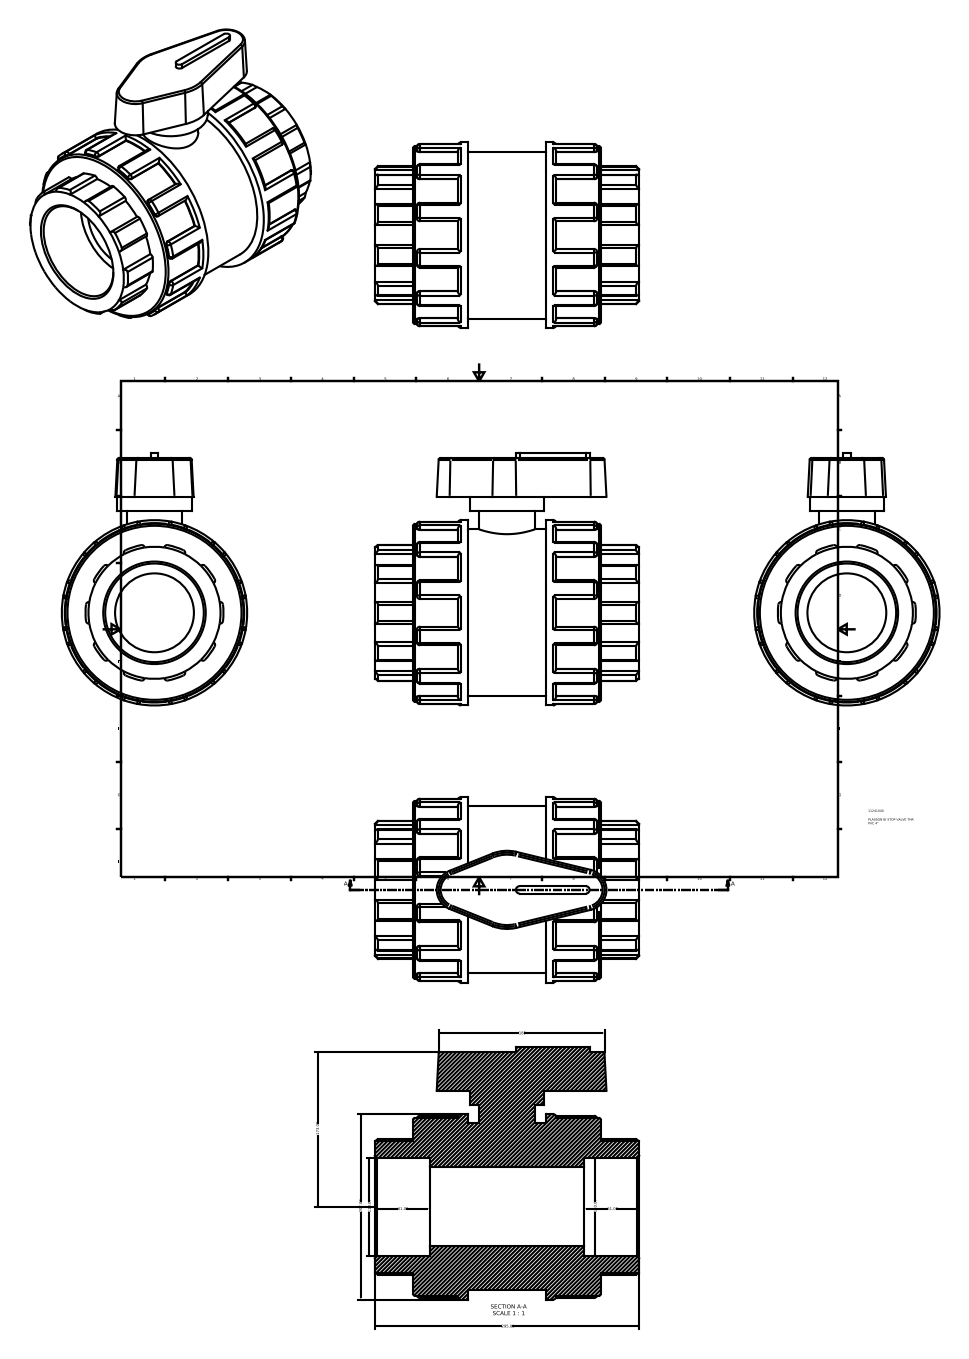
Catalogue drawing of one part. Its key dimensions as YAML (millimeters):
part_name: "11241040"
step_written_by: "Autodesk Inventor 2015 (AUTOMOTIVE_DESIGN)"
units: millimeters
bodies: {solids: 1, faces: 434, planar: 114, cylindrical: 192, other: 128}
overall_size: [295, 281.69, 207]
volume: 6262000
surface_area: 375836
round_holes:
  - {diameter: 88.06, count: 1}
  - {diameter: 110.07, count: 1}
round_bosses_or_shafts:
  - {diameter: 207, count: 1}
  - {diameter: 198.72, count: 1}
  - {diameter: 186.3, count: 1}
  - {diameter: 82.8, count: 1}
  - {diameter: 62.1, count: 1}
partial_cylinders:
  - {radius: 3.3, count: 84}
  - {radius: 2.2, count: 4}
  - {radius: 4.14, count: 2}
  - {radius: 73.75, count: 1}
  - {radius: 77.05, count: 1}
face_to_face_distances: [42.7, 61, 191.3, 252.3, 103.7, 148.6, 209.6, 234, 18.3, 130.3]
